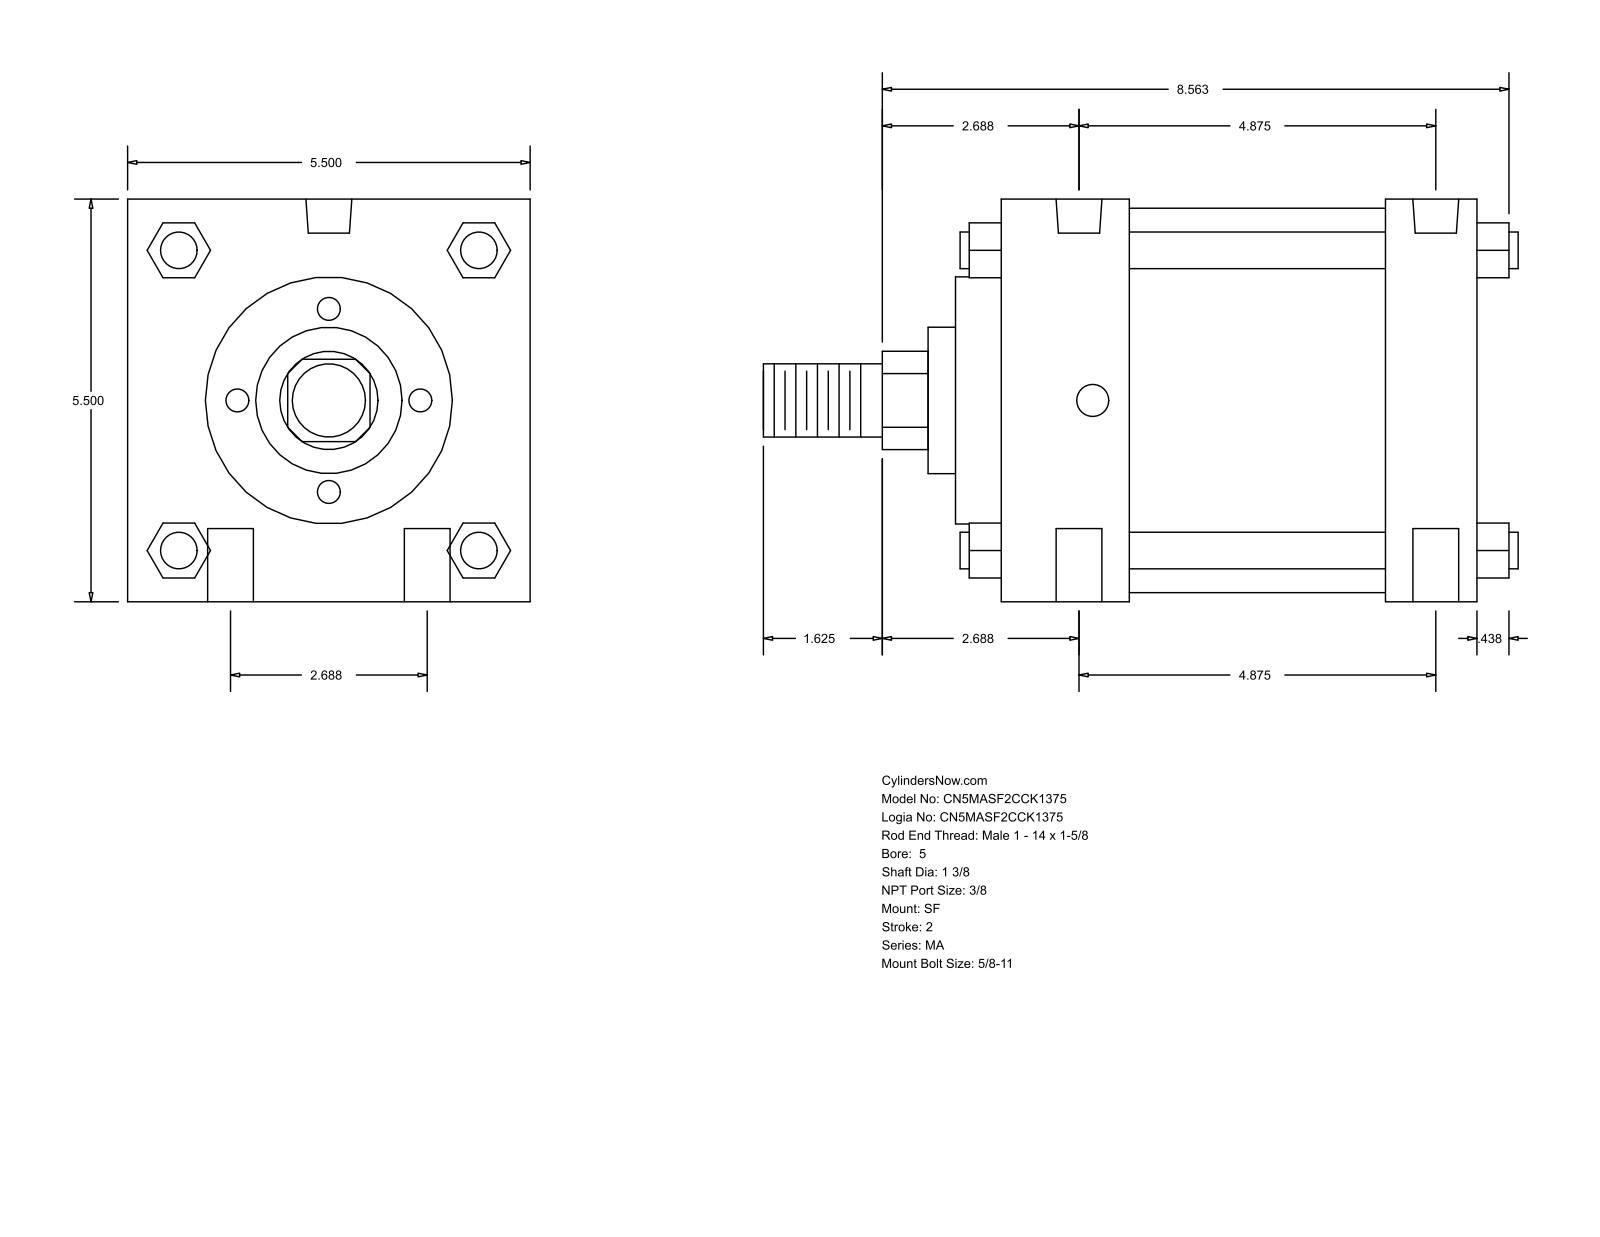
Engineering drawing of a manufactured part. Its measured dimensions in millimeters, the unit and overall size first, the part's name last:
Units: millimetres
Overall size (bounding box): 261.94 × 139.7 × 139.7
Round holes (diameter × count): ⌀15.88 ×4, ⌀11.11 ×2, ⌀15.93 ×2
Round bosses / shafts (diameter × count): ⌀12.7 ×4, ⌀133.35 ×1, ⌀85.72 ×1, ⌀50.8 ×1, ⌀34.92 ×1, ⌀25.4 ×1
Partial cylindrical surfaces — rounded edges, fillets, slot ends (radius × count): R17.06 ×1
Main face-to-face distances: 139.7, 165.11, 44.45, 133.35, 88.9, 120.66, 31.76, 15.87, 60.32, 149.22
Hole centre spacings: 34.13, 128.45, 123.83, 68.26, 141.4, 114.29
Bodies: 0 solids, 126 faces (95 planar, 31 cylindrical, 0 other)
Part name (STEP PRODUCT): MA_SF__0500_1.375
STEP written by: GSSL Pune (CONFIG_CONTROL_DESIGN)
